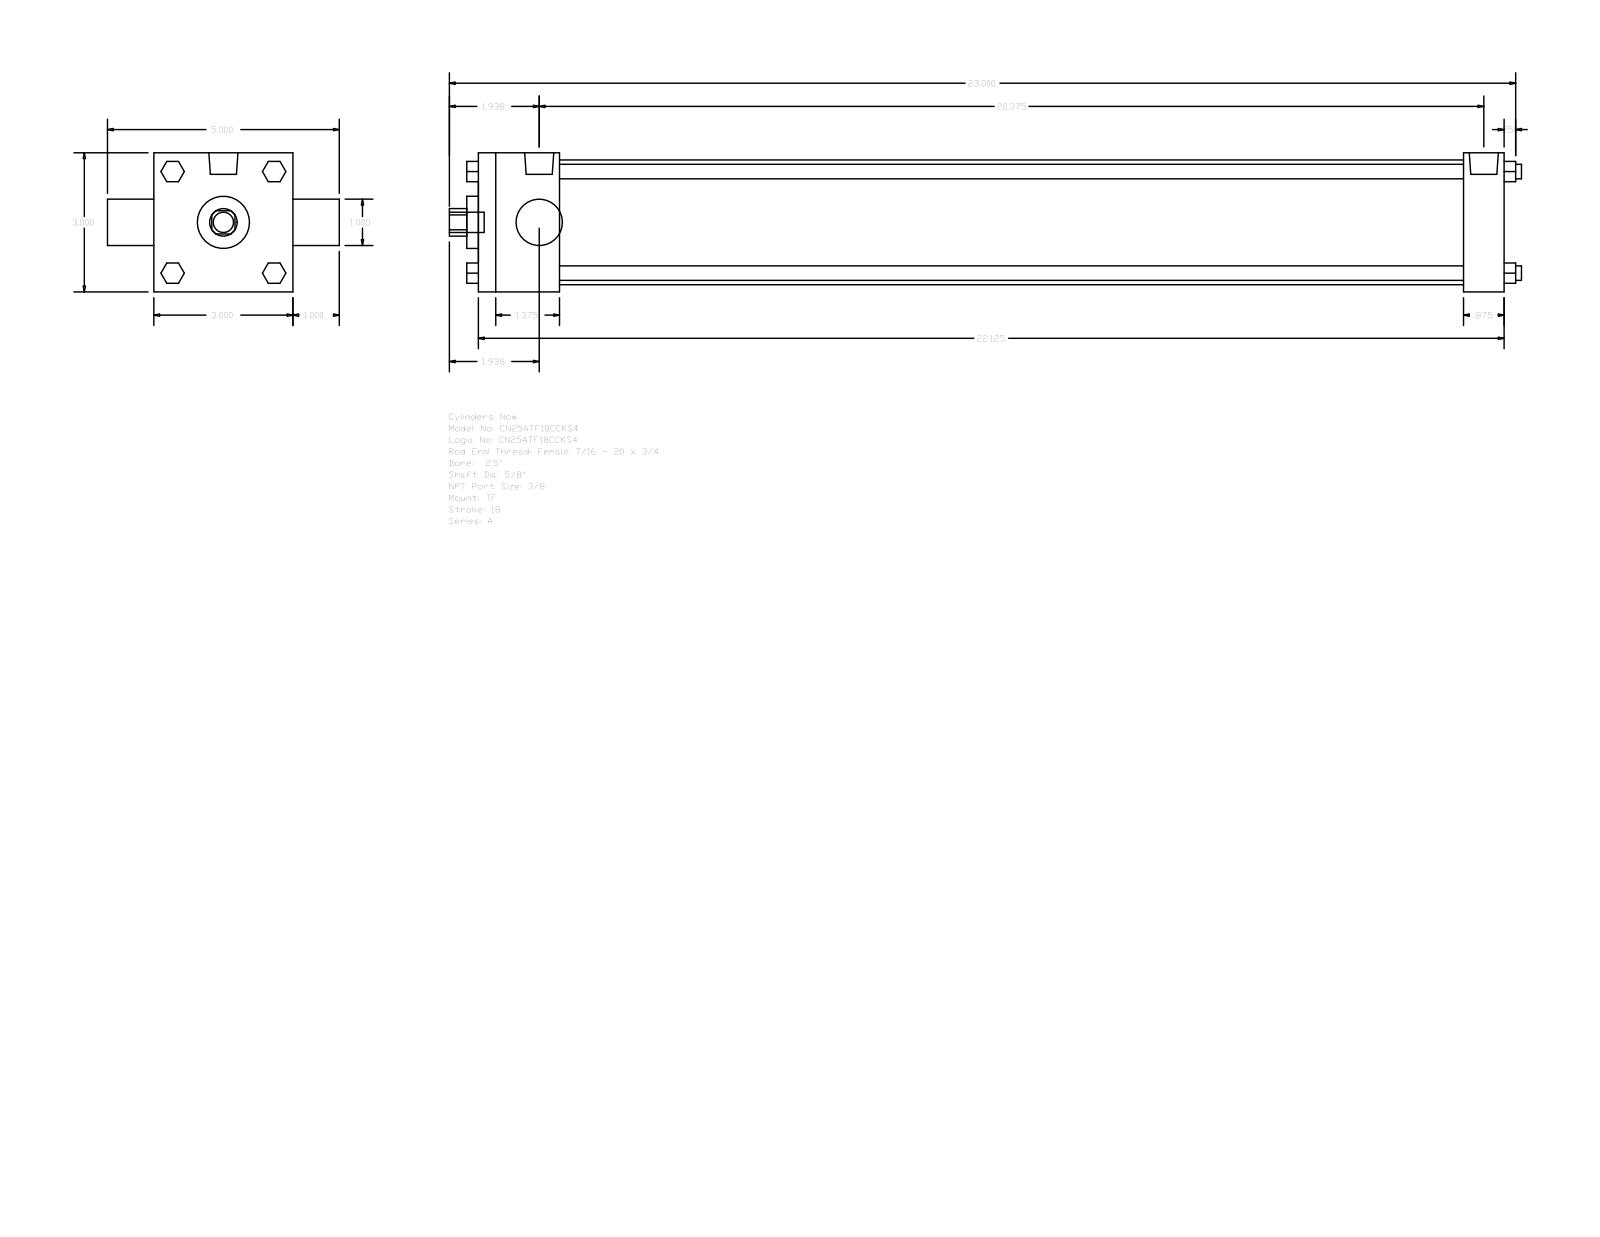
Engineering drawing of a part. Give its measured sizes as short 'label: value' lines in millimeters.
name: A_TF__0250_0.625
written by: GSSL Pune (CONFIG_CONTROL_DESIGN)
unit: mm
bodies: 0 solids, 120 faces (92 planar, 28 cylindrical, 0 other)
size: 587.38 × 127 × 76.2
holes: 1× ⌀15.88, 1× ⌀25.4, 1× ⌀28.57, 1× ⌀68.33
bosses: 4× ⌀7.94, 3× ⌀5.56, 2× ⌀15.93, 1× ⌀11.11
rounds: 1× R7.54
face distances: 76.2, 561.97, 44.45, 539.74, 495.29, 517.52, 22.23, 25.4, 101.6, 6.35
